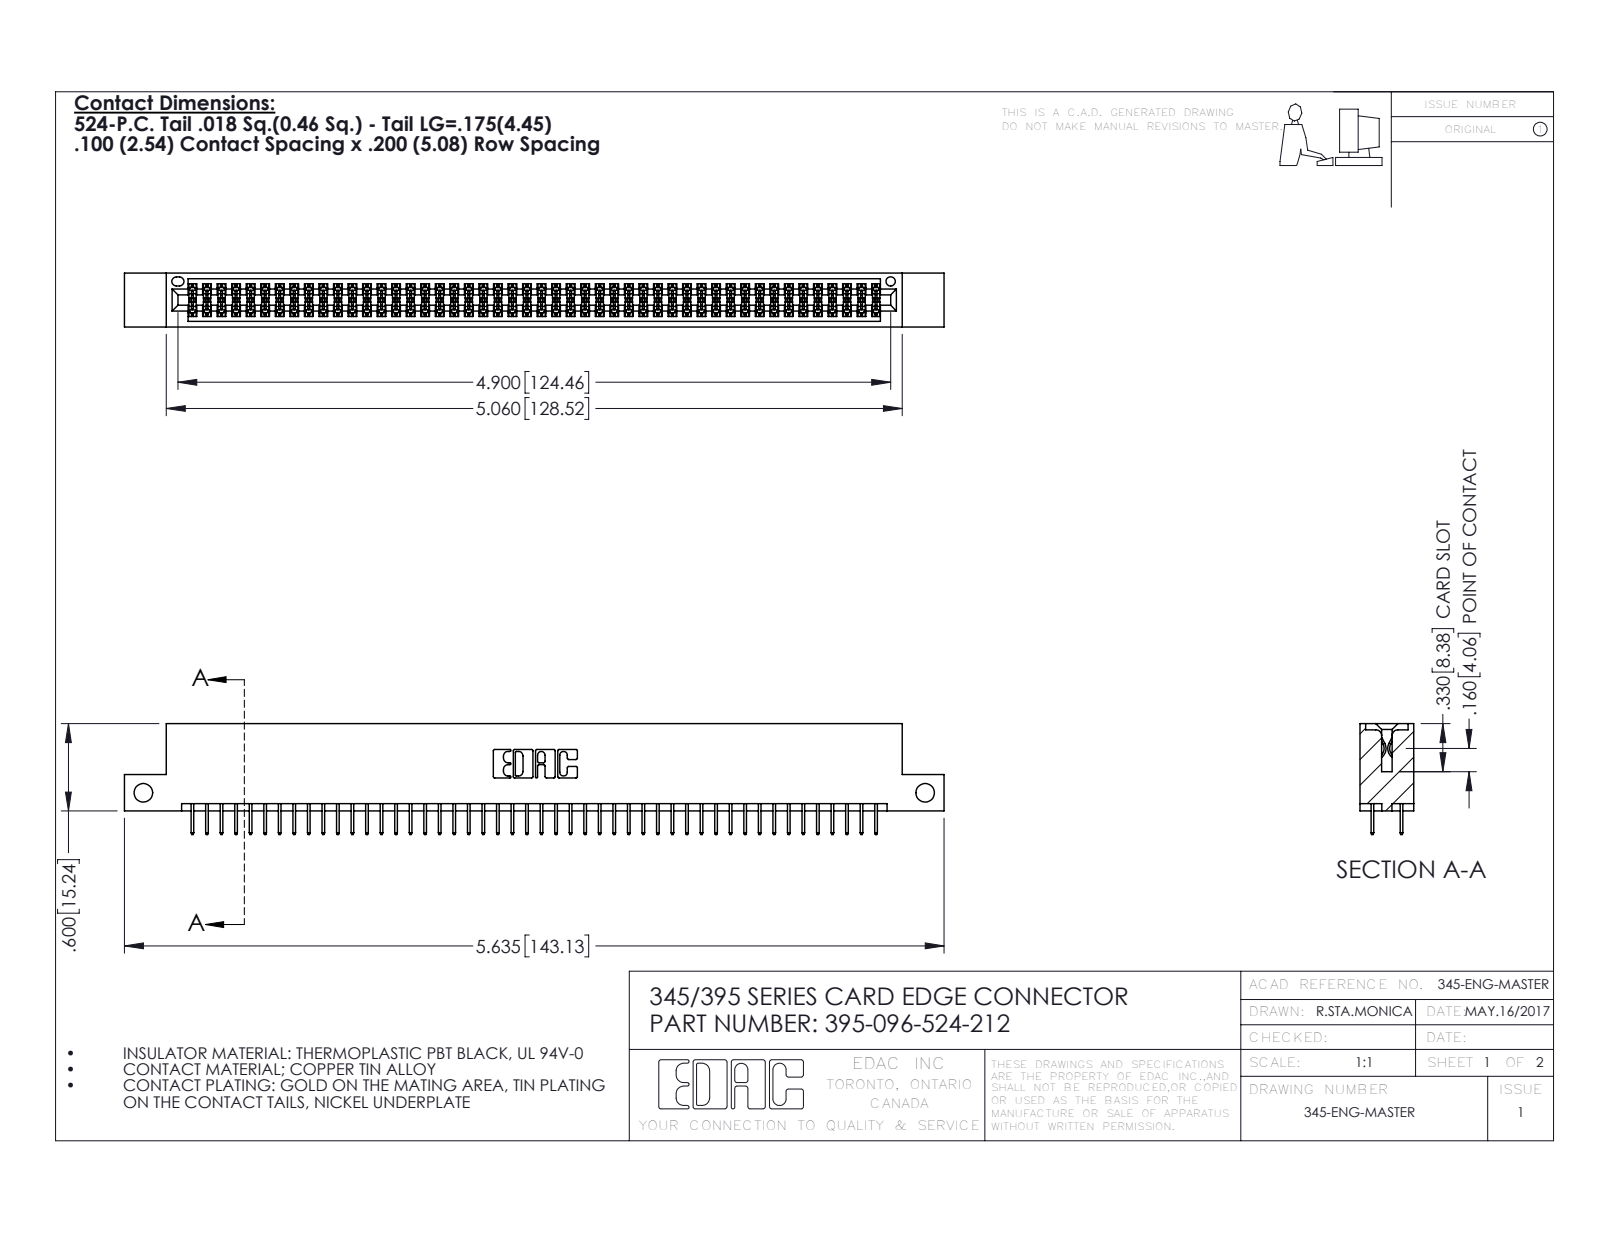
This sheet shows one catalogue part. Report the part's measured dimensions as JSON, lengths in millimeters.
{"part_name": "345 Part_Flush Mounting Lugs - Side Mount; 345-292-001_345-293-124; 395-096-524-212", "step_written_by": "SolidWorks 2016 (CONFIG_CONTROL_DESIGN)", "units": "millimeters", "bodies": {"solids": 97, "faces": 5310, "planar": 3824, "cylindrical": 1486, "other": 0}, "overall_size": [143.1, 19.4, 9.4], "volume_mm3": 13700, "surface_area_mm2": 19890, "round_holes": [[3.3, 2], [1.6, 1]], "partial_cylinders_radius": [[0.2, 144], [0.3, 22], [0.2, 6], [0.8, 6], [0.7, 3], [0.4, 2], [0.5, 2], [0.6, 2]], "face_to_face_distances": [7.6, 1.8, 5.1, 9.4, 2.5, 6.9, 0.6, 5.7, 1.8, 4.4], "hole_center_spacings": [136.5]}
